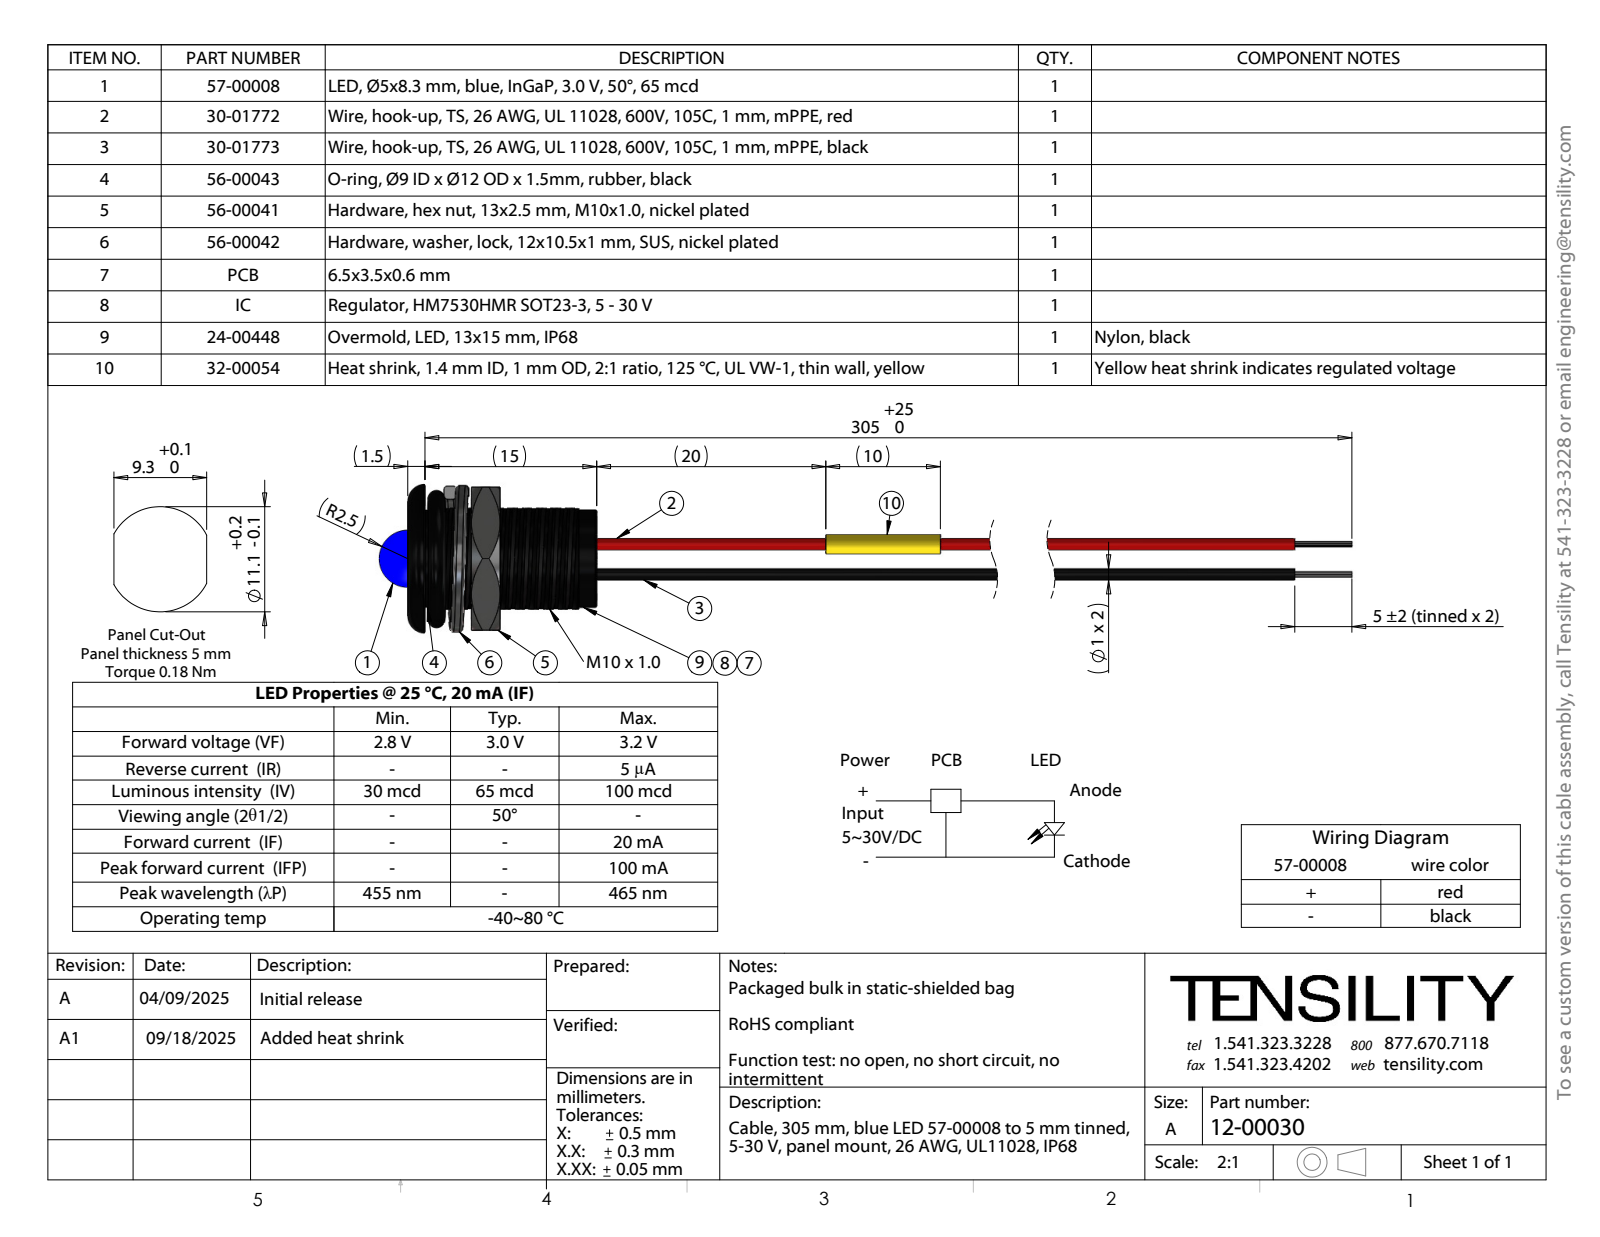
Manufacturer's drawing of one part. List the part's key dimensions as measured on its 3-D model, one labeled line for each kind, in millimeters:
Part name (STEP PRODUCT): 57-00008_trimmed leads; 30-01773_stripped and tinned; 56-00043; 56-00042_Split washer (+4 more)
STEP written by: SolidWorks 2021 (CONFIG_CONTROL_DESIGN)
Units: millimetres
Bodies: 57 solids, 514 faces (185 planar, 246 cylindrical, 83 other)
Overall size (bounding box): 173.99 × 14.43 × 12.99
Volume: 1 769 mm³ · Surface area: 6 568 mm²
Round holes (diameter × count): ⌀1 ×2
Round bosses / shafts (diameter × count): ⌀1 ×2, ⌀0.83 ×2, ⌀8.5 ×1, ⌀5 ×1
Partial cylindrical surfaces — rounded edges, fillets, slot ends (radius × count): R4.33 ×1, R5 ×1
Main face-to-face distances: 1.5, 16.5, 15, 12.5, 8.06, 6.56, 8.44, 5.56, 4.06, 2.5
Hole centre spacings: 0.36, 0.38, 0.33, 2.43, 2.35, 2.48, 2.52, 2.56
